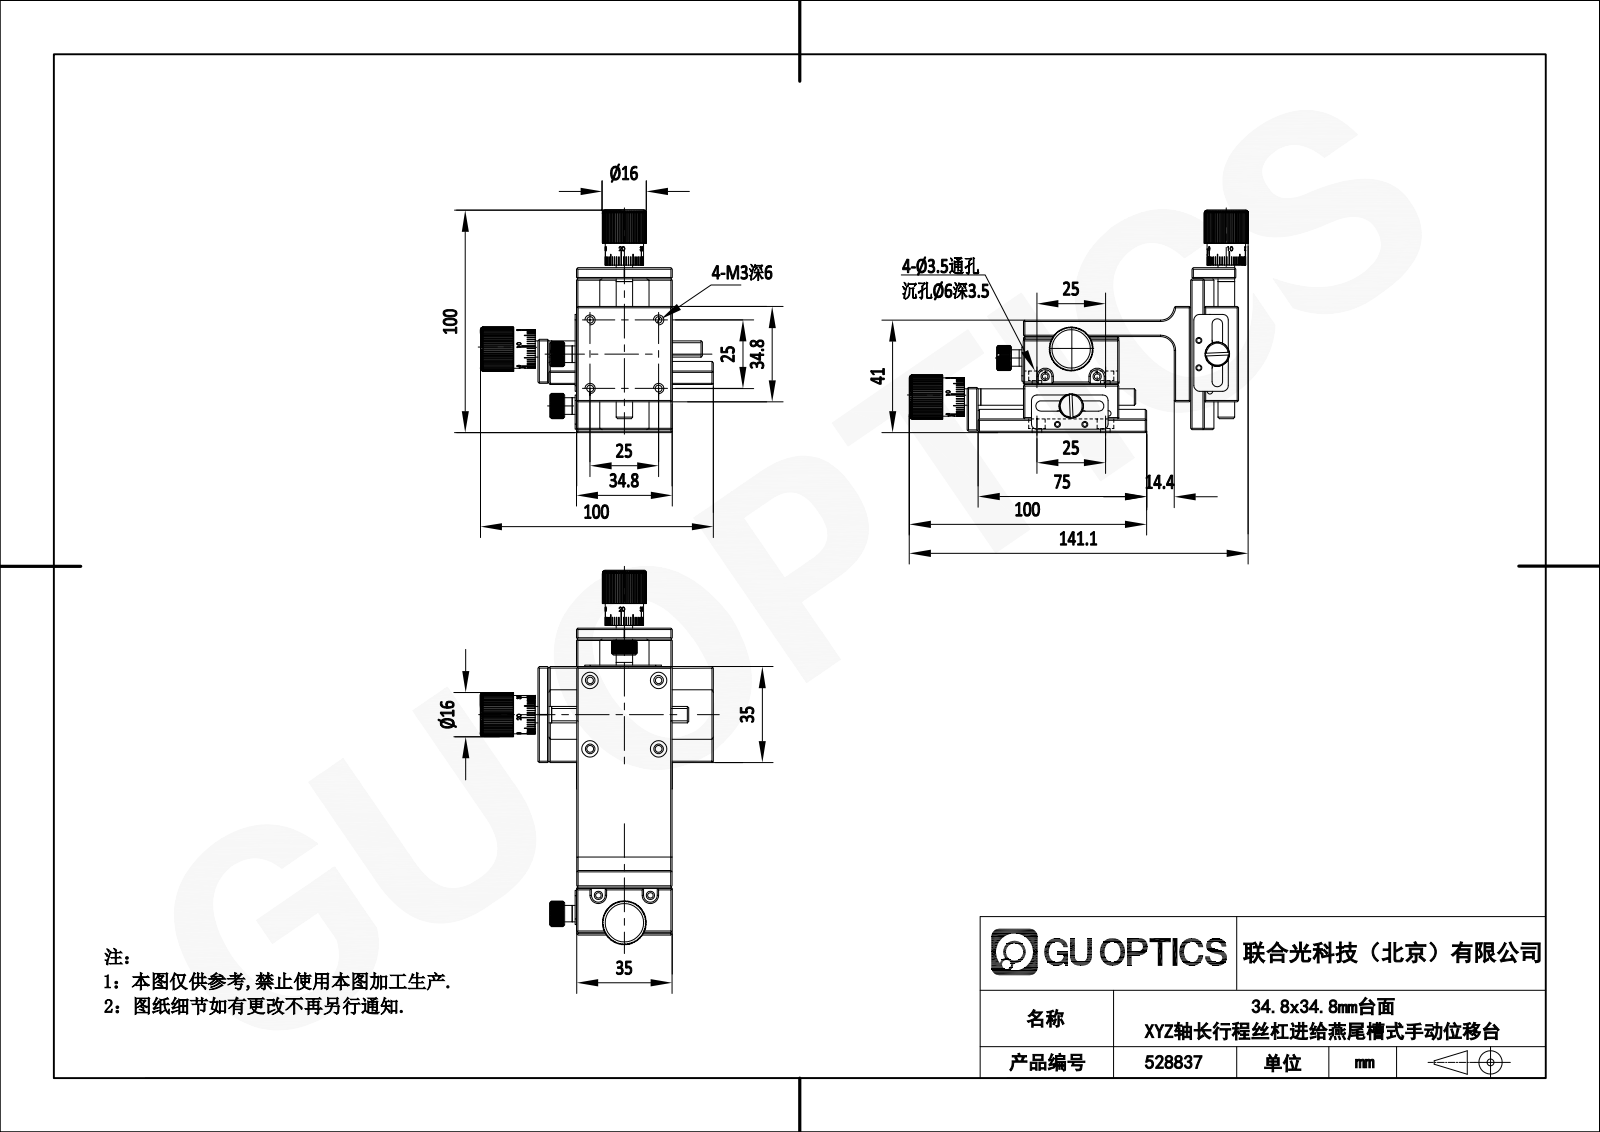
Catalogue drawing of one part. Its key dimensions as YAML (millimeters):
part_name: "528837"
step_written_by: "SolidWorks 2020 (CONFIG_CONTROL_DESIGN)"
units: millimeters
bodies: {solids: 60, faces: 2673, planar: 1278, cylindrical: 655, other: 740}
overall_size: [139.6, 99.5, 99.5]
volume: 126922
surface_area: 75423
round_holes:
  - {diameter: 1.6, count: 24}
  - {diameter: 2.05, count: 15}
  - {diameter: 2.5, count: 13}
  - {diameter: 3.4, count: 10}
  - {diameter: 6, count: 10}
  - {diameter: 3, count: 9}
  - {diameter: 1.5, count: 6}
  - {diameter: 2.2, count: 6}
  - {diameter: 2.4, count: 6}
  - {diameter: 3.5, count: 3}
  - {diameter: 4.1, count: 3}
  - {diameter: 5, count: 3}
round_bosses_or_shafts:
  - {diameter: 2, count: 15}
  - {diameter: 4.5, count: 9}
  - {diameter: 4, count: 9}
  - {diameter: 3, count: 7}
  - {diameter: 3.8, count: 6}
  - {diameter: 2.5, count: 6}
  - {diameter: 5.5, count: 4}
  - {diameter: 13, count: 3}
partial_cylinders:
  - {radius: 0.3, count: 24}
  - {radius: 2, count: 18}
  - {radius: 0.5, count: 12}
  - {radius: 0.6, count: 12}
  - {radius: 1.8, count: 6}
  - {radius: 2.5, count: 6}
  - {radius: 3, count: 3}
  - {radius: 7.25, count: 3}
face_to_face_distances: [17.5, 5, 12.5, 3.5, 8.5, 34.9, 9, 35, 23.5, 6]
hole_center_spacings: [9, 25, 2.85, 3, 5.25, 5.5, 8.39, 10.77]
